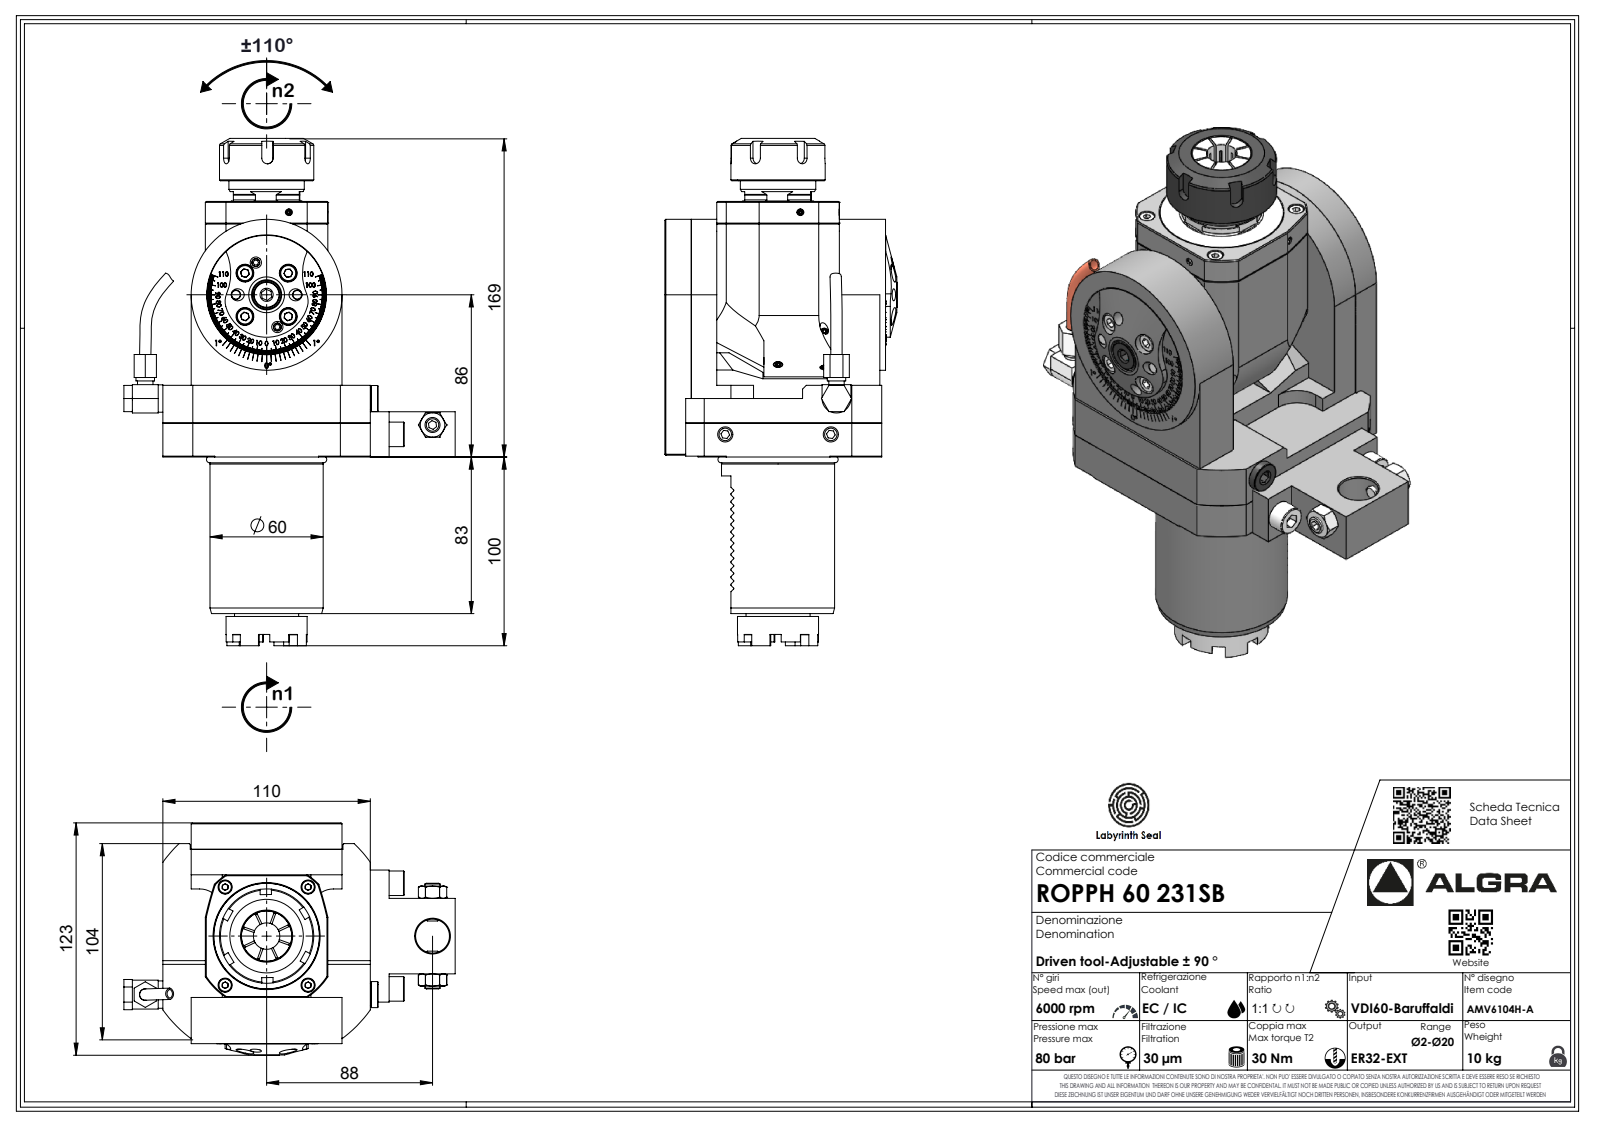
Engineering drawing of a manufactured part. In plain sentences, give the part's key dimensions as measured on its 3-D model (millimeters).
The part is named "ROPPH60231SB". Its 3-D file was written by "SolidWorks 2023 (AUTOMOTIVE_DESIGN)". It is 1 solid with 669 faces: 426 planar, 115 cylindrical and 128 other. Overall it measures 268.91 by 175.7 by 123 millimeters. Its volume is 1 468 000 cubic millimeters and its surface area 125 873 square millimeters. Round holes: 1 of diameter 2.1. Round bosses or shafts: 1 of diameter 80, 1 of diameter 60, 1 of diameter 58.7, 1 of diameter 50, 1 of diameter 43, 1 of diameter 40, 1 of diameter 34, 1 of diameter 14.5. Partial cylindrical surfaces (rounded edges, fillets, slot ends): 19 of radius 0.2, 14 of radius 0.3, 7 of radius 0.33, 7 of radius 0.52, 7 of radius 3.7, 5 of radius 3, 2 of radius 10, 2 of radius 12. The main face-to-face distances are 22.5, 87.5, 65, 80, 7.5, 95, 7, 15, 27.5, 72.5.
